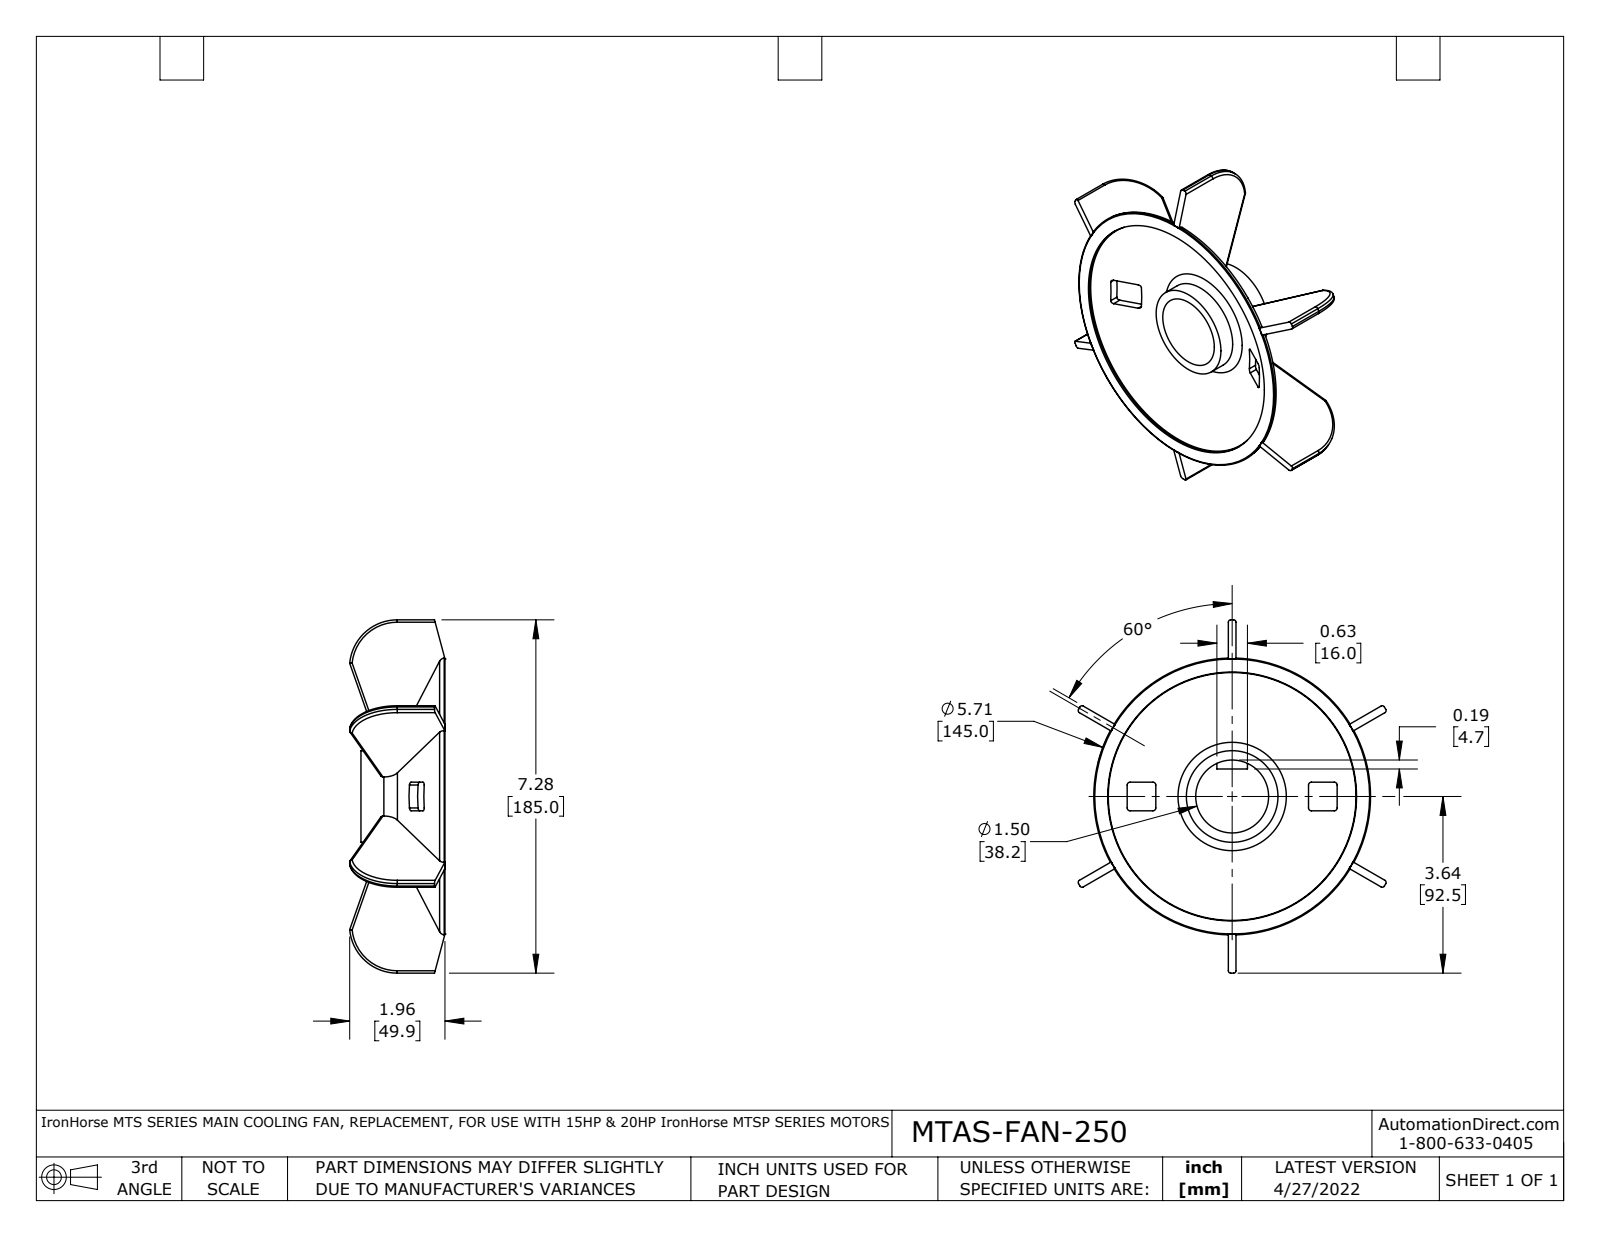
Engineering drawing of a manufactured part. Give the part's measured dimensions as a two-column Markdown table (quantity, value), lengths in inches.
| quantity | value |
| --- | --- |
| part name | FAN (250T) nc coord fxt |
| STEP written by | SolidWorks 2021 (AUTOMOTIVE_DESIGN) |
| units | inches |
| bodies | 1 solid, 145 faces (44 planar, 54 cylindrical, 47 other) |
| overall size | 7.283 × 6.35 × 1.965 |
| volume | 8.499 in³ |
| surface area | 108.1 in² |
| round holes (diameter × count) | 1.504 × 1, 5.131 × 1 |
| round bosses / shafts (diameter × count) | 1.89 × 1 |
| partial cylindrical surfaces (radius × count) | 0.049 × 24, 0.059 × 8, 0.02 × 6, 0.984 × 6 |
| main face-to-face distances | 0.157, 1.732, 1.378, 0.354, 0.591, 0.236, 0.394, 0.272, 0.862, 1.26 |
